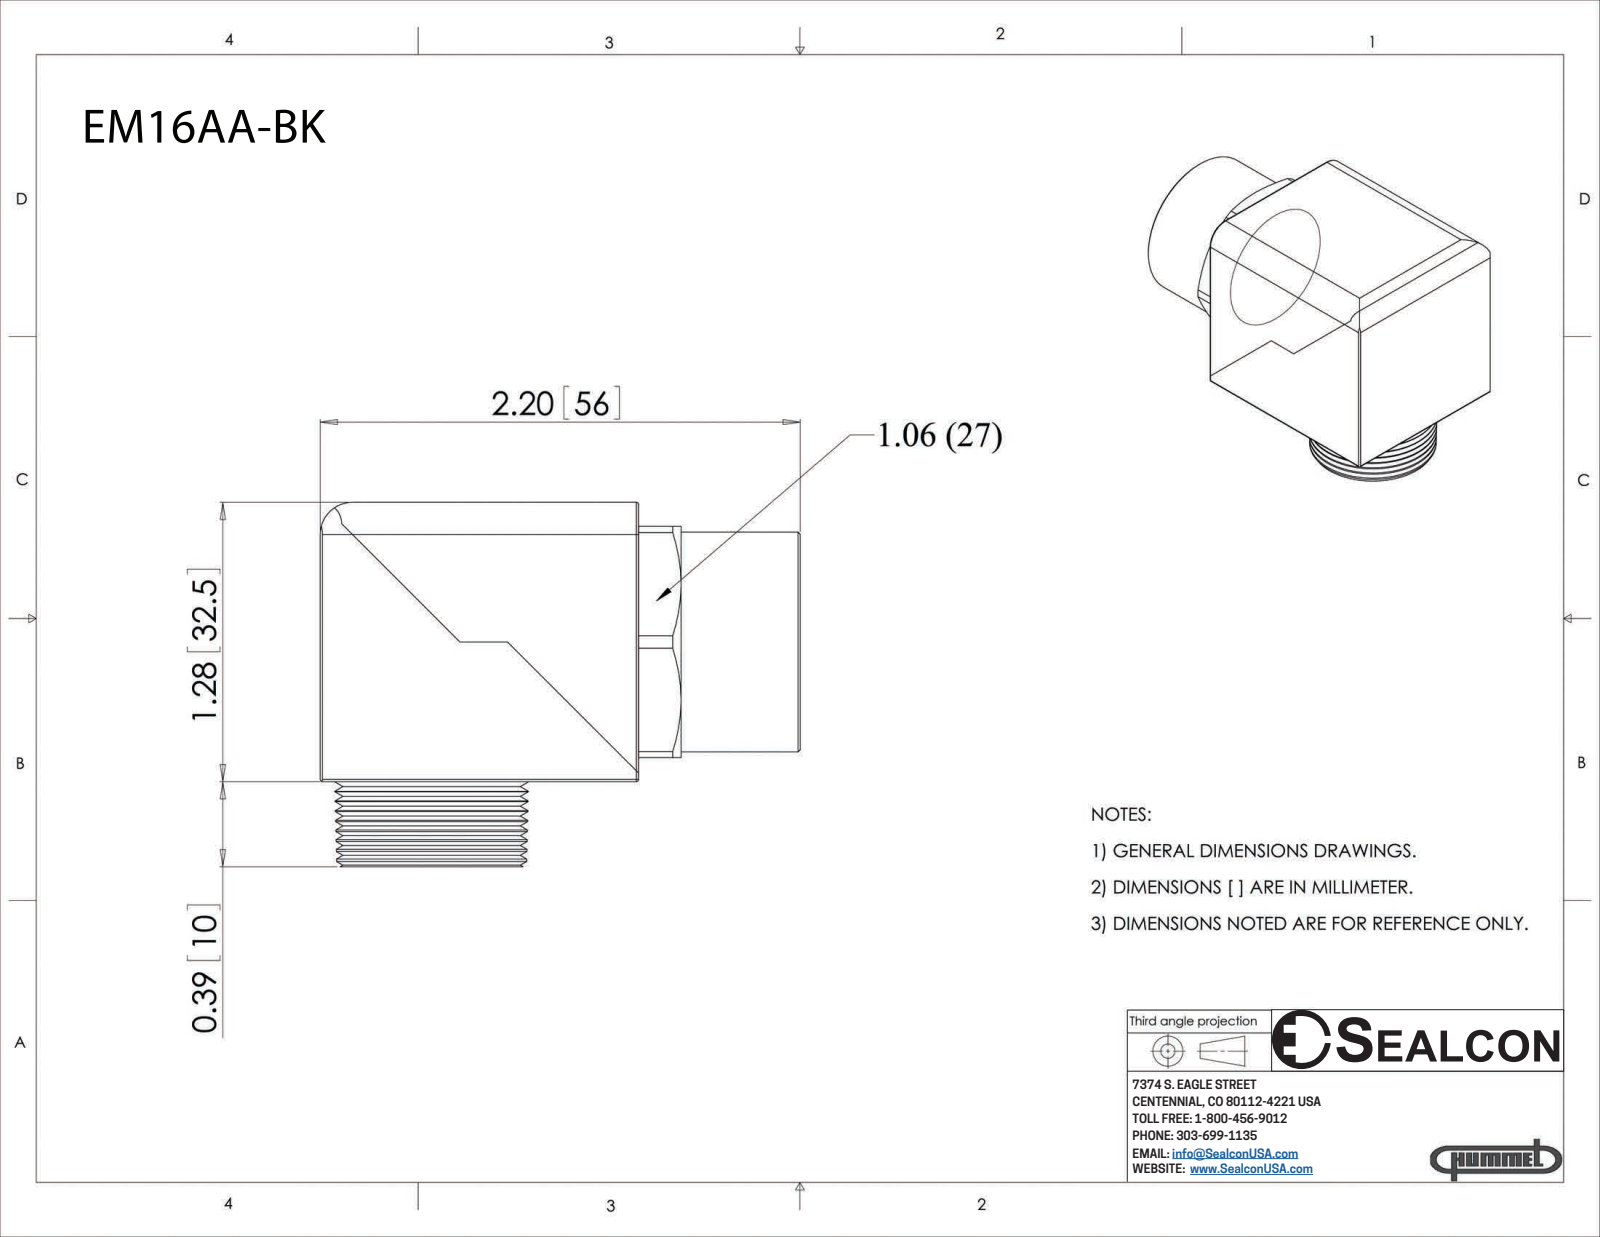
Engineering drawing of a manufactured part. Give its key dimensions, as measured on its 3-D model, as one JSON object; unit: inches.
{"part_name": "EM16AA-BK", "step_written_by": "SolidWorks 2007 (AUTOMOTIVE_DESIGN)", "units": "inches", "bodies": {"solids": 2, "faces": 136, "planar": 31, "cylindrical": 34, "other": 71}, "overall_size": [2.2, 1.67, 1.28], "volume_in3": 2.466, "surface_area_in2": 24, "round_holes": [[0.49, 2], [0.88, 1]], "round_bosses_or_shafts": [[1.007, 1]], "partial_cylinders_radius": [[0.01, 7], [0.147, 3], [0.098, 1], [0.596, 1]], "face_to_face_distances": [1.28, 0.155, 1.459, 0.64, 0.195, 1.654, 0.195, 1.459, 0.39, 1.03]}
